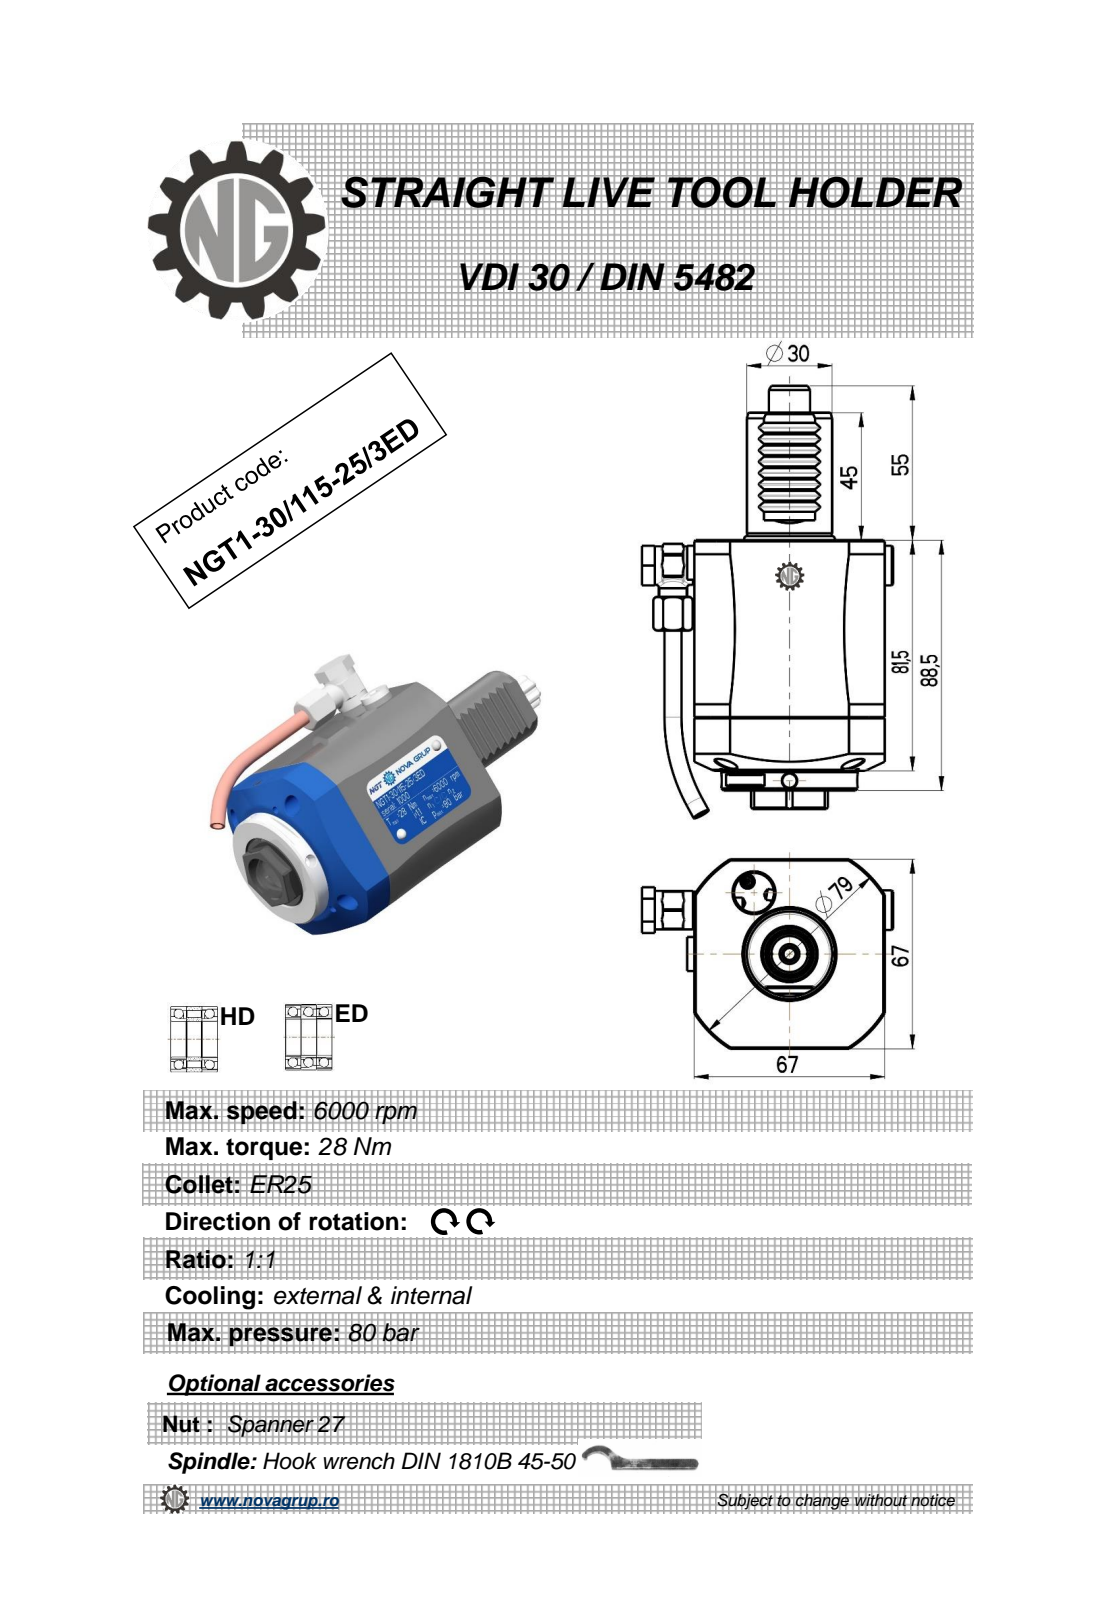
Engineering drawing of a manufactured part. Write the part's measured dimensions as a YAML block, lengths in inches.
part_name: "NGT1_30_115_25_3HD"
step_written_by: "PRO/ENGINEER BY PARAMETRIC TECHNOLOGY CORPORATION, 2010280 (CONFIG_CONTROL_DESIGN)"
units: inches
bodies: {solids: 2, faces: 396, planar: 132, cylindrical: 133, other: 131}
overall_size: [6.037, 3.48, 2.638]
volume: 23.44
surface_area: 63.52
round_holes:
  - {diameter: 0.157, count: 3}
  - {diameter: 0.197, count: 2}
  - {diameter: 0.118, count: 1}
  - {diameter: 0.165, count: 1}
  - {diameter: 0.209, count: 1}
  - {diameter: 0.236, count: 1}
  - {diameter: 0.244, count: 1}
  - {diameter: 0.354, count: 1}
  - {diameter: 0.394, count: 1}
  - {diameter: 0.433, count: 1}
  - {diameter: 0.709, count: 1}
  - {diameter: 1.043, count: 1}
round_bosses_or_shafts:
  - {diameter: 1.89, count: 1}
  - {diameter: 1.181, count: 1}
  - {diameter: 0.551, count: 1}
  - {diameter: 0.535, count: 1}
  - {diameter: 0.512, count: 1}
  - {diameter: 0.472, count: 1}
  - {diameter: 0.394, count: 1}
  - {diameter: 0.335, count: 1}
partial_cylinders:
  - {radius: 0.115, count: 16}
  - {radius: 0.012, count: 8}
  - {radius: 0.016, count: 6}
  - {radius: 0.02, count: 4}
  - {radius: 0.224, count: 1}
  - {radius: 0.285, count: 1}
  - {radius: 0.303, count: 1}
  - {radius: 1.555, count: 1}
face_to_face_distances: [2.638, 3.484, 0.276, 3.209, 0.111, 5.256, 4.98, 1.772, 0.472, 0.256]
hole_center_spacings: [0.016, 1.726, 1.741, 3.054]
